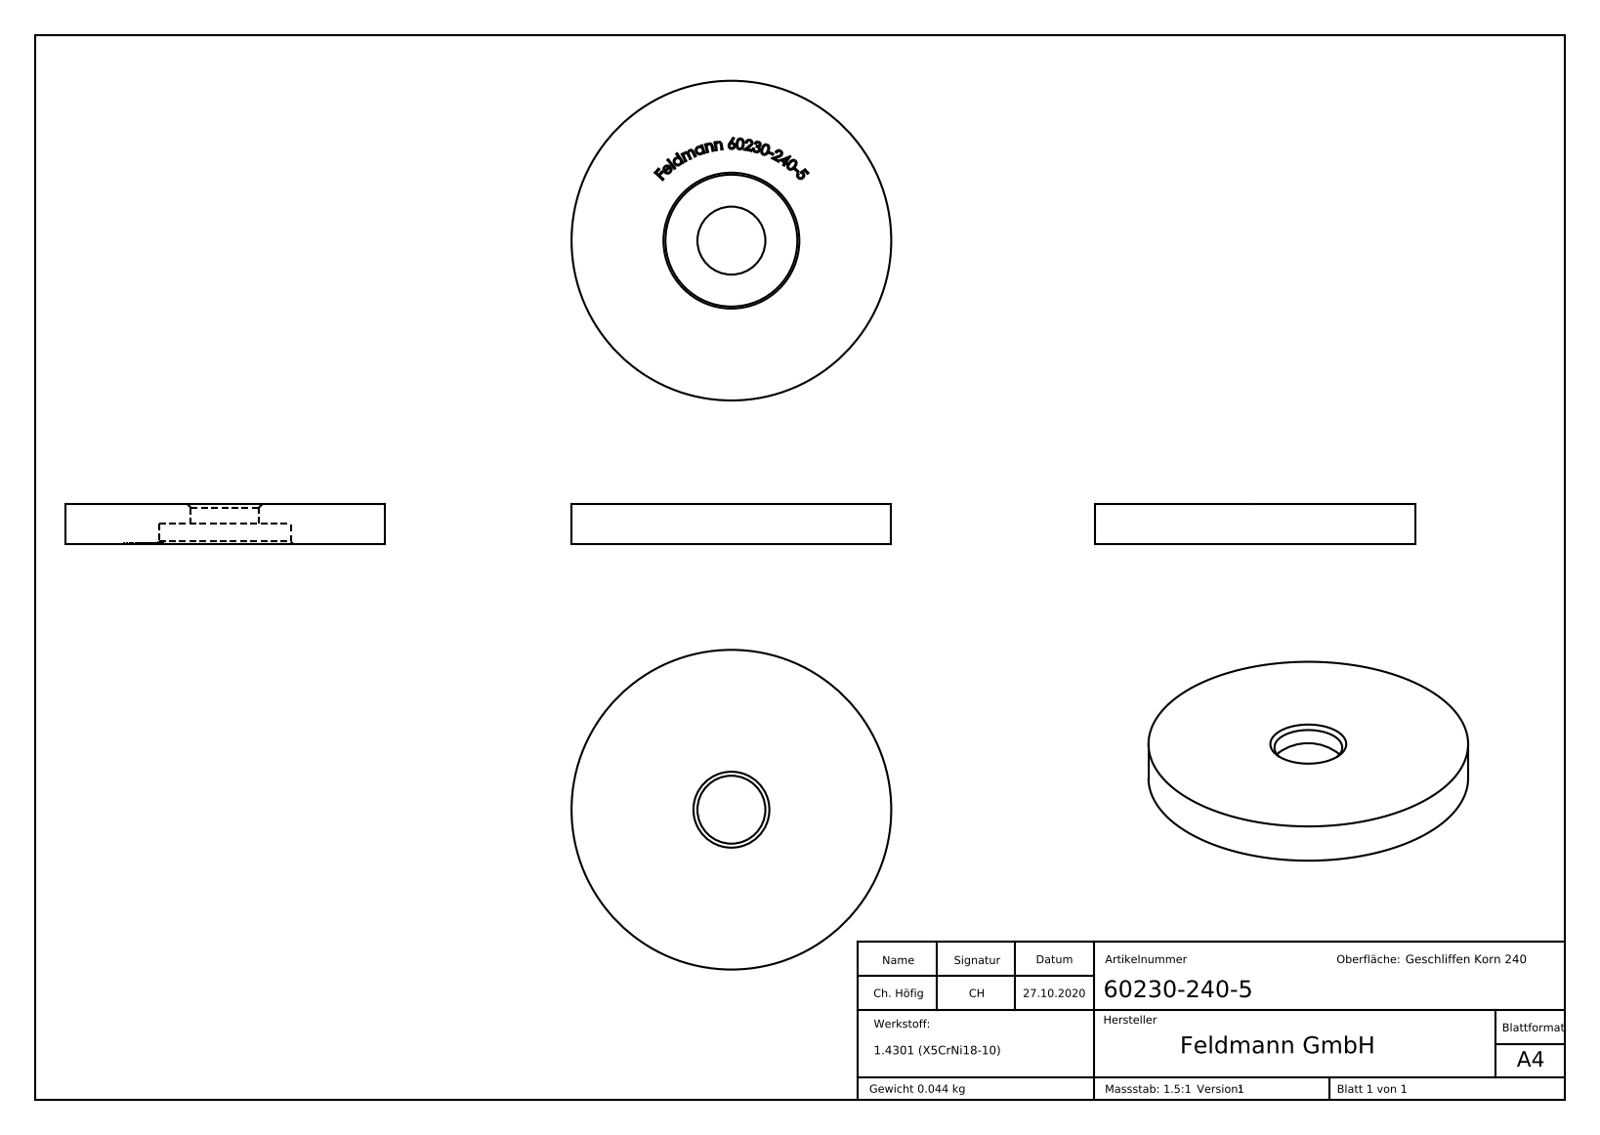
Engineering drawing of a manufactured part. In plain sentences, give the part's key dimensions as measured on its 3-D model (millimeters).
The part is named "60230-240-5". Its 3-D file was written by "SolidWorks 2018 (CONFIG_CONTROL_DESIGN)". It is 1 solid with 257 faces: 129 planar, 6 cylindrical and 122 other. Overall it measures 40 by 40 by 5 millimeters. Its volume is 5 601 cubic millimeters and its surface area 3 220 square millimeters. Round holes: 1 of diameter 8.5, 1 of diameter 16.5. Round bosses or shafts: 1 of diameter 40. The main face-to-face distances are 5, 2.5, 2.4, 4.9, 0.54, 1.33, 0.85, 0.73, 0.72, 0.6.
